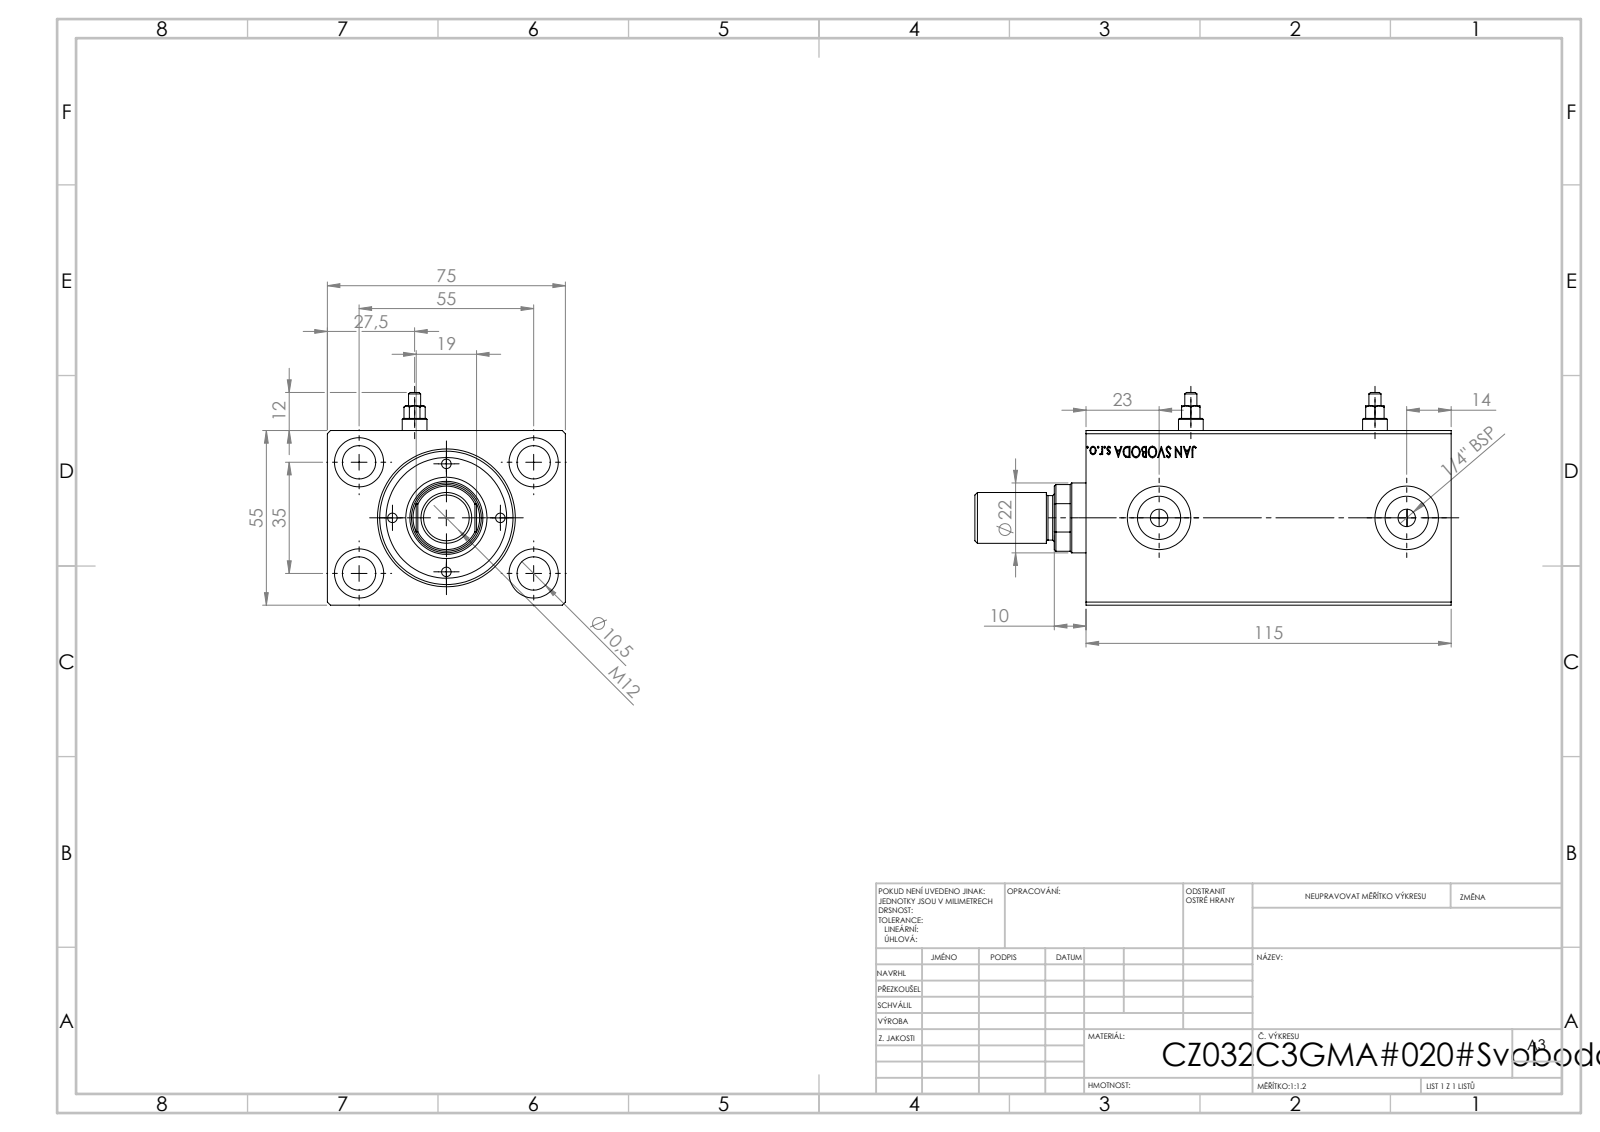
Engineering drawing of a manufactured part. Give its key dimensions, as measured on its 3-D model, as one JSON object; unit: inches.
{"step_written_by": "SolidWorks 2019 (CONFIG_CONTROL_DESIGN)", "units": "inches", "bodies": {"solids": 1, "faces": 824, "planar": 396, "cylindrical": 46, "other": 382}, "overall_size": [4.528, 2.953, 2.165], "volume_in3": 20.39, "surface_area_in2": 101.7, "round_holes": [[0.413, 4], [0.61, 4], [0.217, 2], [0.315, 2], [0.535, 2], [0.787, 2], [1.26, 1], [1.417, 1], [1.654, 1]], "face_to_face_distances": [2.165, 2.953, 4.528, 4.52, 0.407, 4.121, 3.984, 0.535, 0.543, 0.394], "hole_center_spacings": [1.283, 1.378, 2.165, 2.567, 2.283, 3.071]}
